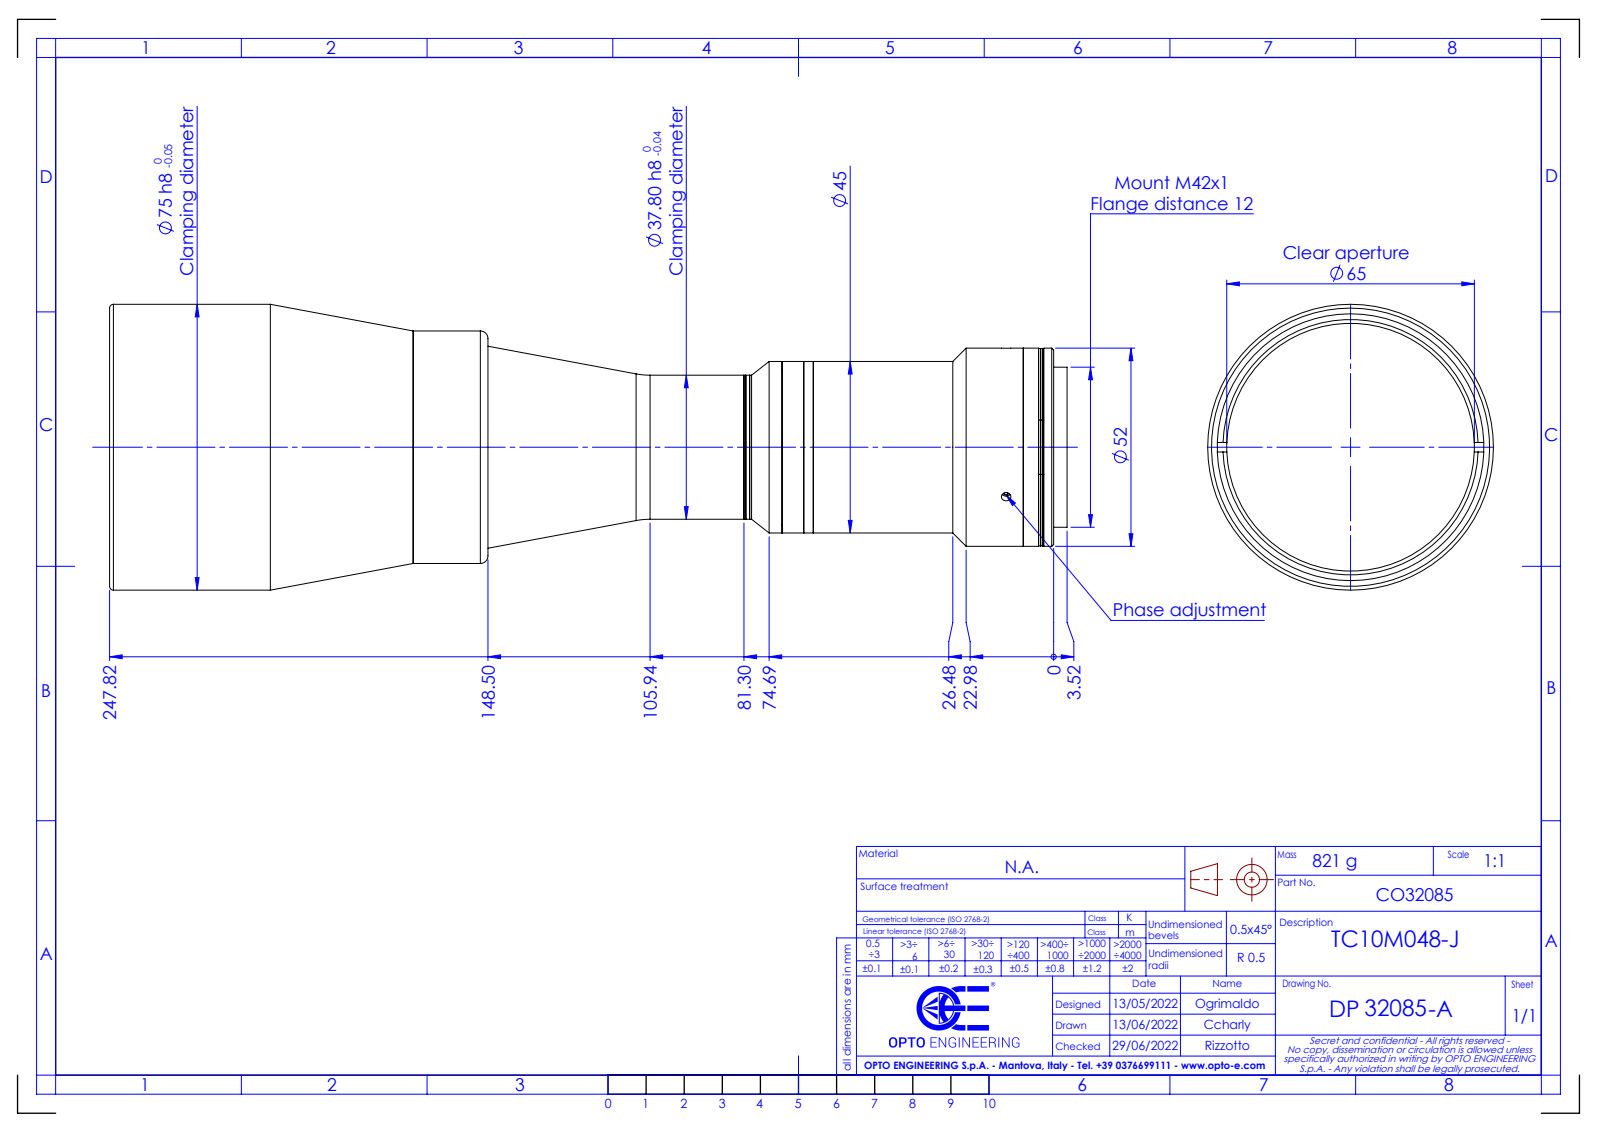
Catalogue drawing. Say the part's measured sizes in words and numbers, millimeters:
The part is named "DP32085-A_TC10M048-J". Its 3-D file was written by "SolidWorks 2021 (CONFIG_CONTROL_DESIGN)". It is 0 solids with 108 faces: 30 planar, 54 cylindrical and 24 other. Overall it measures 251.34 by 75 by 75 millimeters. Round holes: 3 of diameter 2.5, 1 of diameter 38, 1 of diameter 41, 1 of diameter 53, 1 of diameter 65, 1 of diameter 70. Round bosses or shafts: 1 of diameter 75, 1 of diameter 61, 1 of diameter 52, 1 of diameter 51.8, 1 of diameter 45, 1 of diameter 42, 1 of diameter 37.8. The main face-to-face distances are 77.24, 75.82, 1.42, 79.8, 3.98, 2.56, 76.82, 1, 0.42, 2.98.
